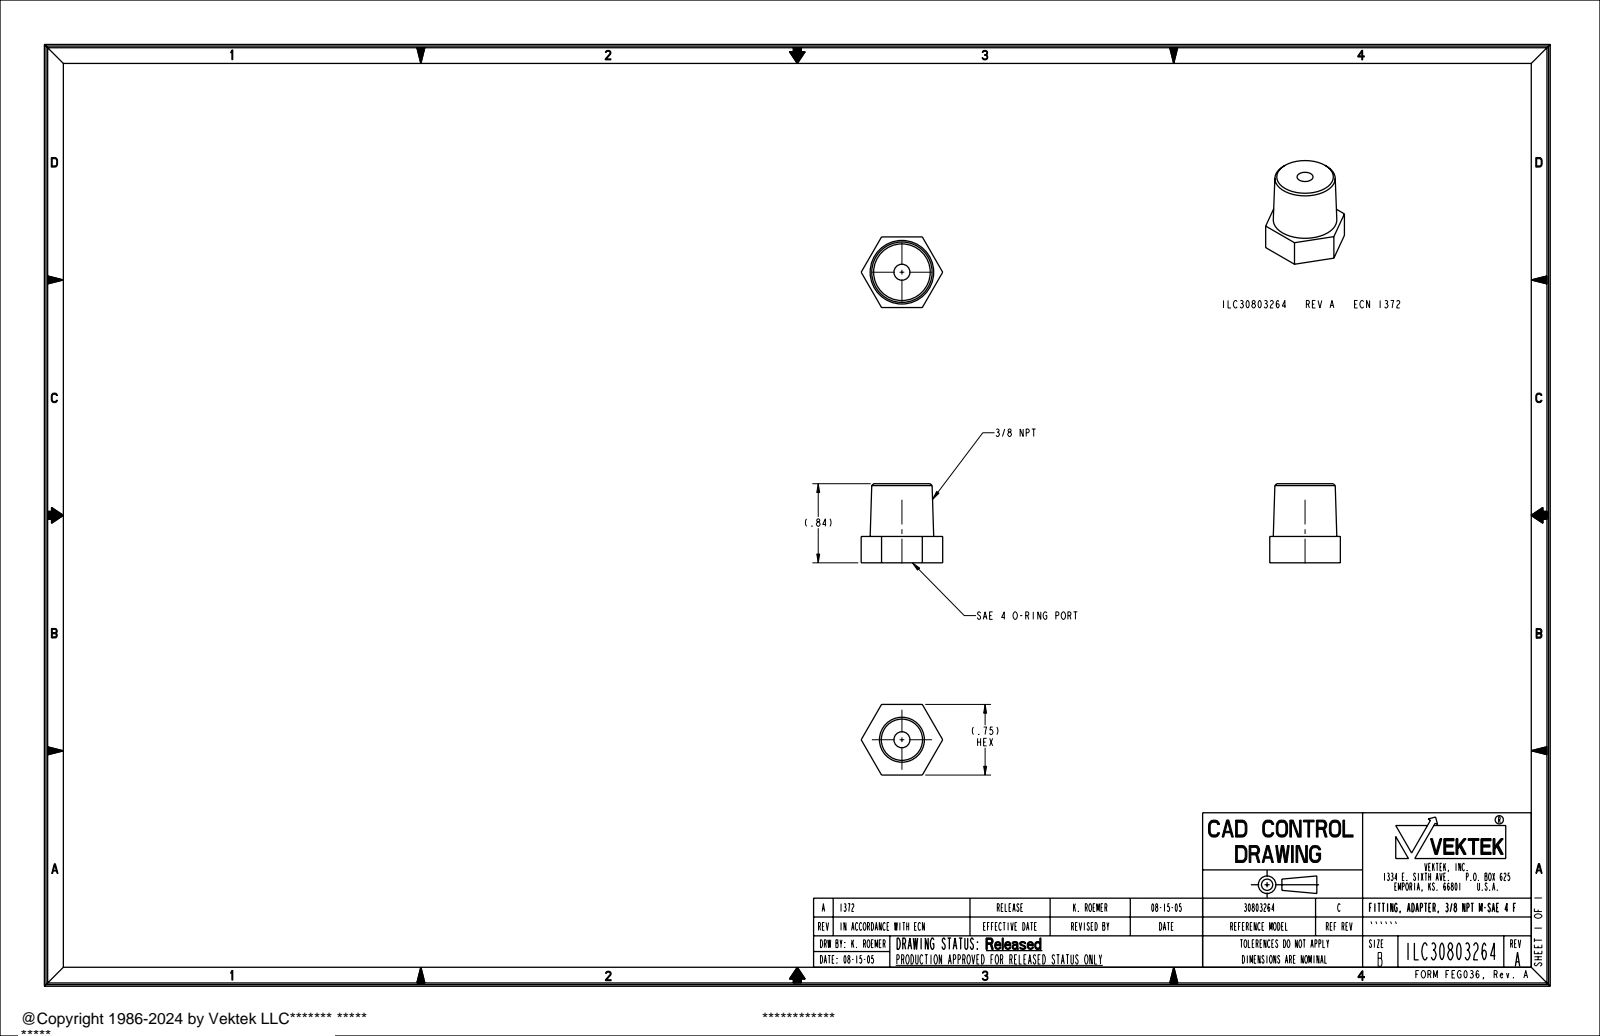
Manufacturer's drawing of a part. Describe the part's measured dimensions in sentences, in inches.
The part is named "ILC30803264". Its 3-D file was written by "PRO/ENGINEER BY PARAMETRIC TECHNOLOGY CORPORATION, 2004290 (AUTOMOTIVE_DESIGN_CC2)". It is 1 solid with 20 faces: 10 planar, 4 cylindrical and 6 other. Overall it measures 0.866 by 0.84 by 0.75 inches. Its volume is 0.233 cubic inches and its surface area 3.664 square inches. Round holes: 1 of diameter 0.17, 1 of diameter 0.438. The main face-to-face distances are 0.75, 0.84, 0.28, 0.56, 0.57, 0.29, 0.27.
